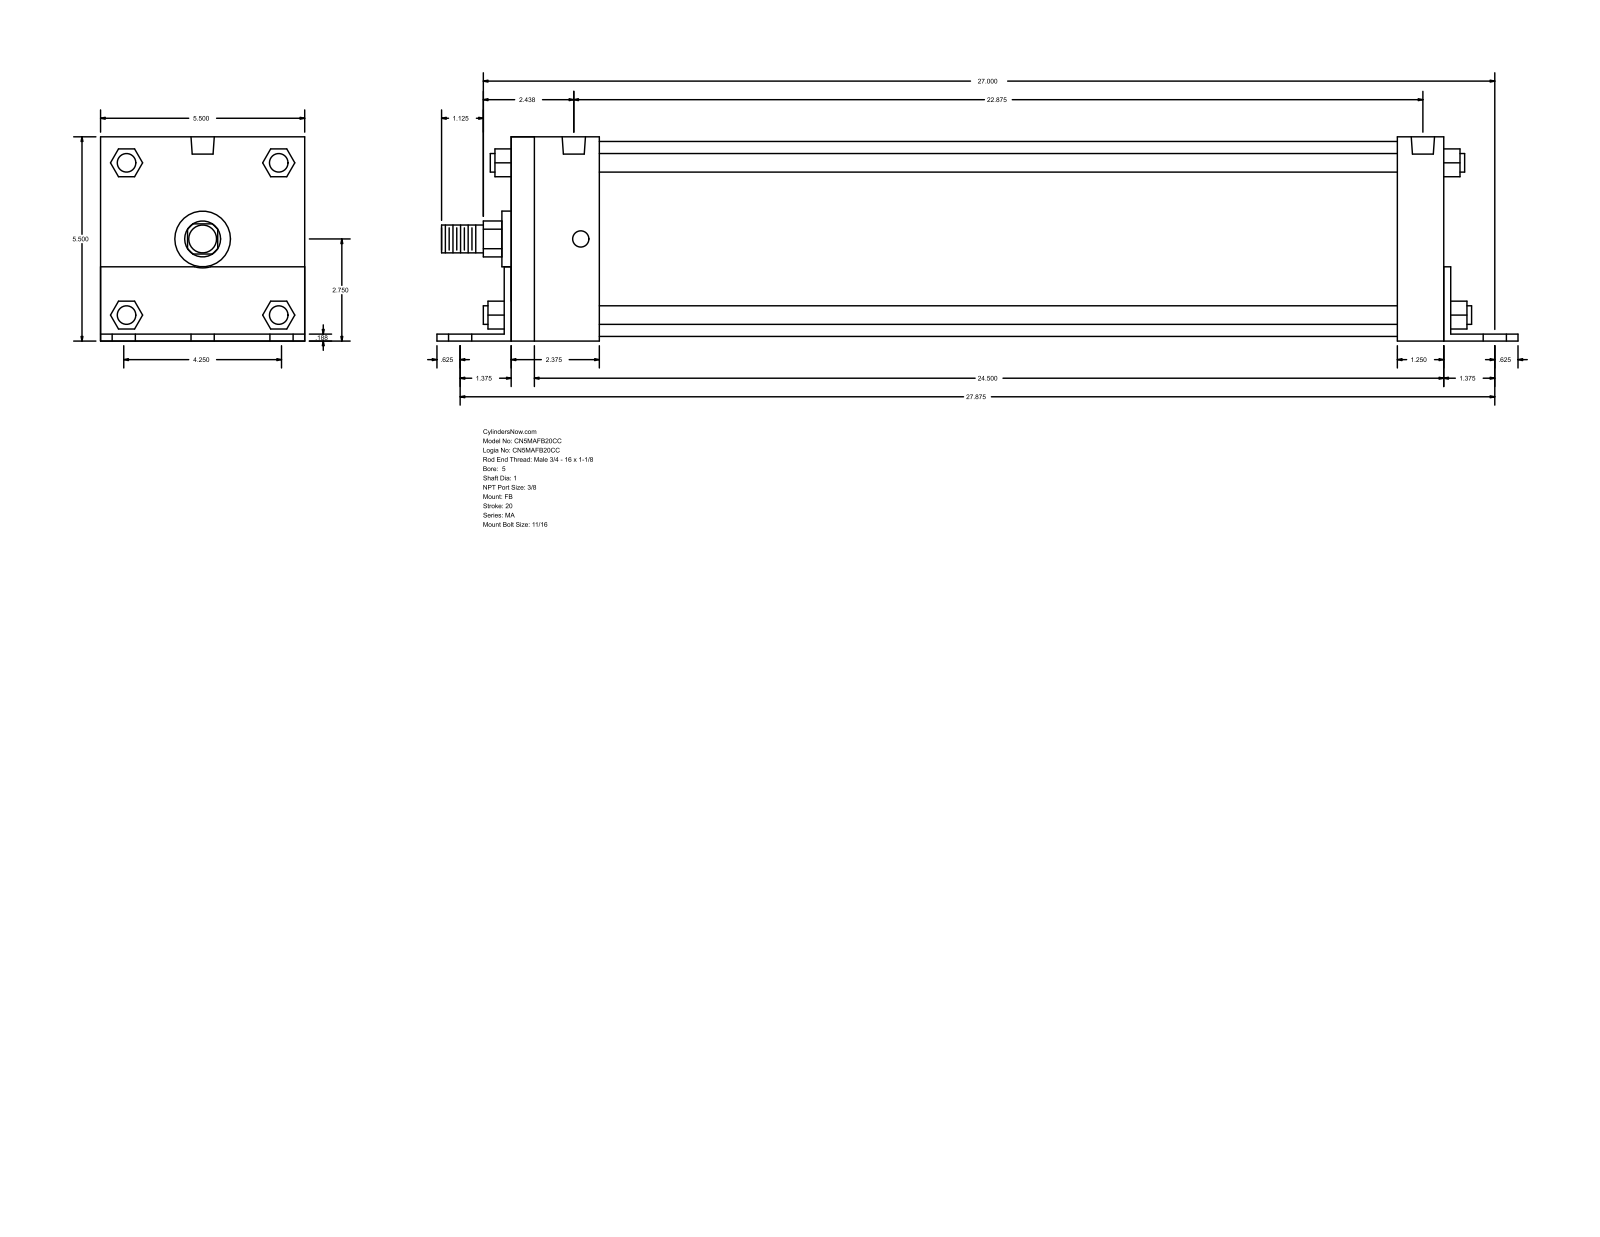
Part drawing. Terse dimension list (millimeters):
name: MA_FB__0500_1
written by: GSSL Pune (CONFIG_CONTROL_DESIGN)
unit: mm
bodies: 0 solids, 140 faces (105 planar, 35 cylindrical, 0 other)
size: 739.77 × 139.75 × 139.7
holes: 6× ⌀17.46, 4× ⌀11.11, 2× ⌀15.93
bosses: 4× ⌀12.7, 1× ⌀133.35, 1× ⌀38.1, 1× ⌀25.4, 1× ⌀19.05
rounds: 1× R12.29, 1× R19.81
face distances: 139.7, 4.76, 139.75, 642.94, 4.71, 134.99, 638.18, 647.7, 36.51, 31.75
hole spacings: 53.98, 710.08, 708.03, 73.04, 76.34, 94.68, 98.63, 107.96
